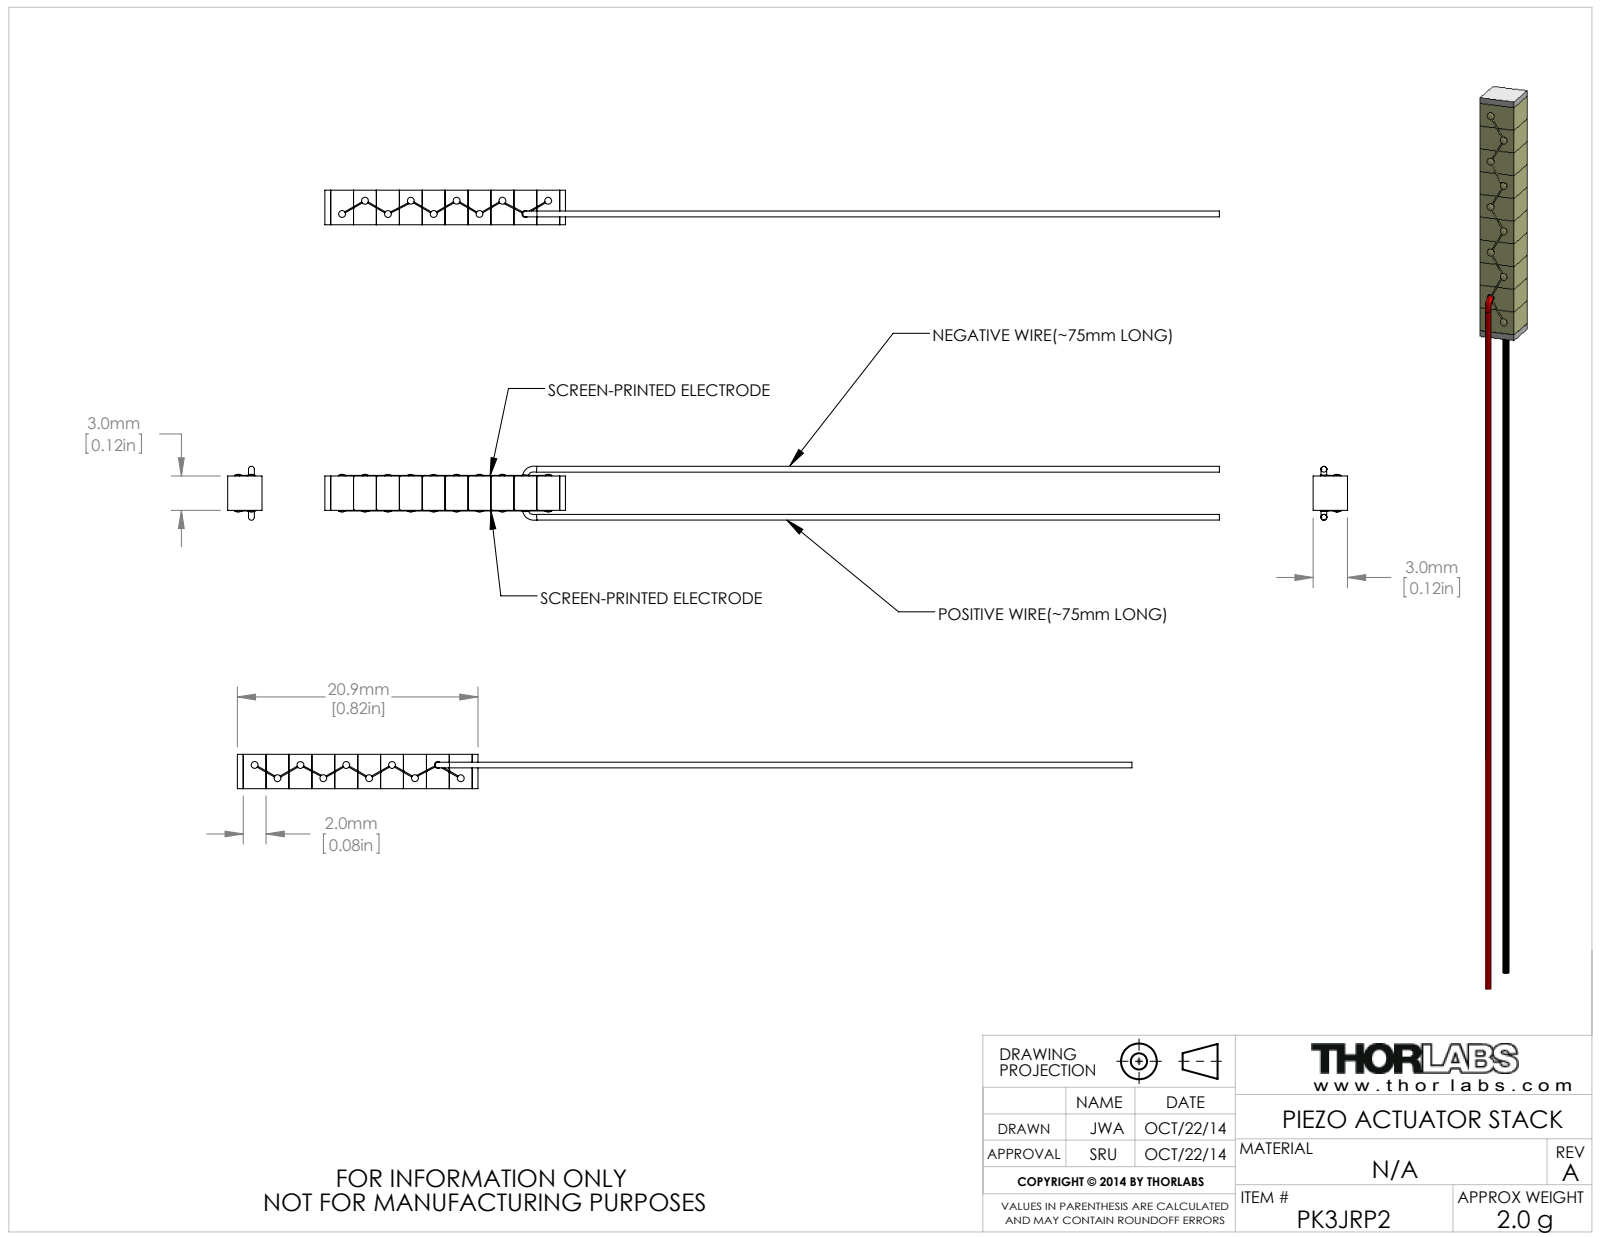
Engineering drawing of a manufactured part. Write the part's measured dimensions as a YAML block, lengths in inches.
part_name: "PK3JRP2"
step_written_by: "SolidWorks 2012 (AUTOMOTIVE_DESIGN)"
units: inches
bodies: {solids: 6, faces: 237, planar: 100, cylindrical: 96, other: 41}
overall_size: [3.075, 0.186, 0.118]
volume: 0.013
surface_area: 1.04
round_bosses_or_shafts:
  - {diameter: 0.024, count: 10}
face_to_face_distances: [0.079, 0.157, 0.236, 0.118, 0.315, 0.394, 0.472, 0.551, 0.63, 0.709]
